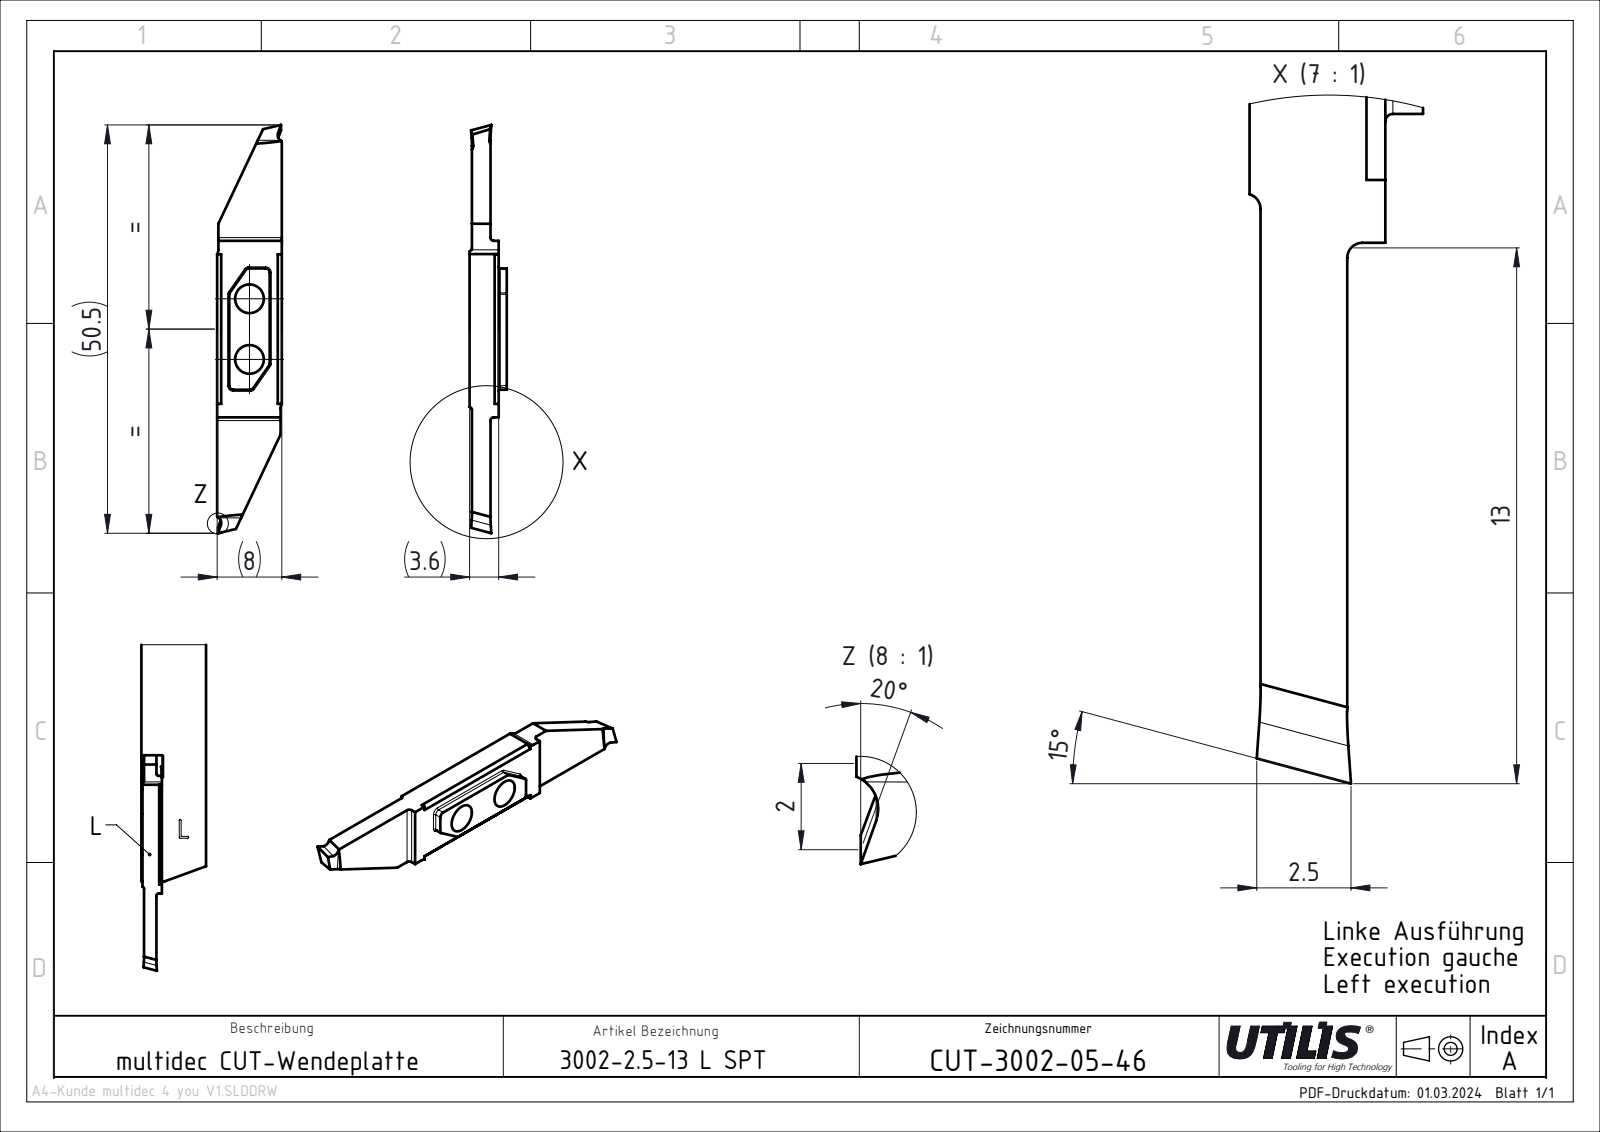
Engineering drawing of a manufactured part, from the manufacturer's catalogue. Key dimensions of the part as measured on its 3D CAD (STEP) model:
Part name (STEP PRODUCT): CUT-3002 SPT Slim_and_Deep; ASME Y14.5
STEP written by: SolidWorks 2023 SP4 || FormatWorks Professional (AP242_MANAGED_MODEL_BASED_3D_ENGINEERING_MIM_LF)
Units: millimetres
Bodies: 1 solid, 36 faces (26 planar, 10 cylindrical, 0 other)
Overall size (bounding box): 50.5 × 8 × 3.6
Volume: 899 mm³ · Surface area: 1 003 mm²
Round holes (diameter × count): ⌀3.55 ×2
Partial cylindrical surfaces — rounded edges, fillets, slot ends (radius × count): R0.4 ×4, R1 ×2
Main face-to-face distances: 2.3, 3.31, 1.01, 2.59, 3.6, 8, 18.09, 7.85, 7.7, 21.82
Hole centre spacings: 7.5
